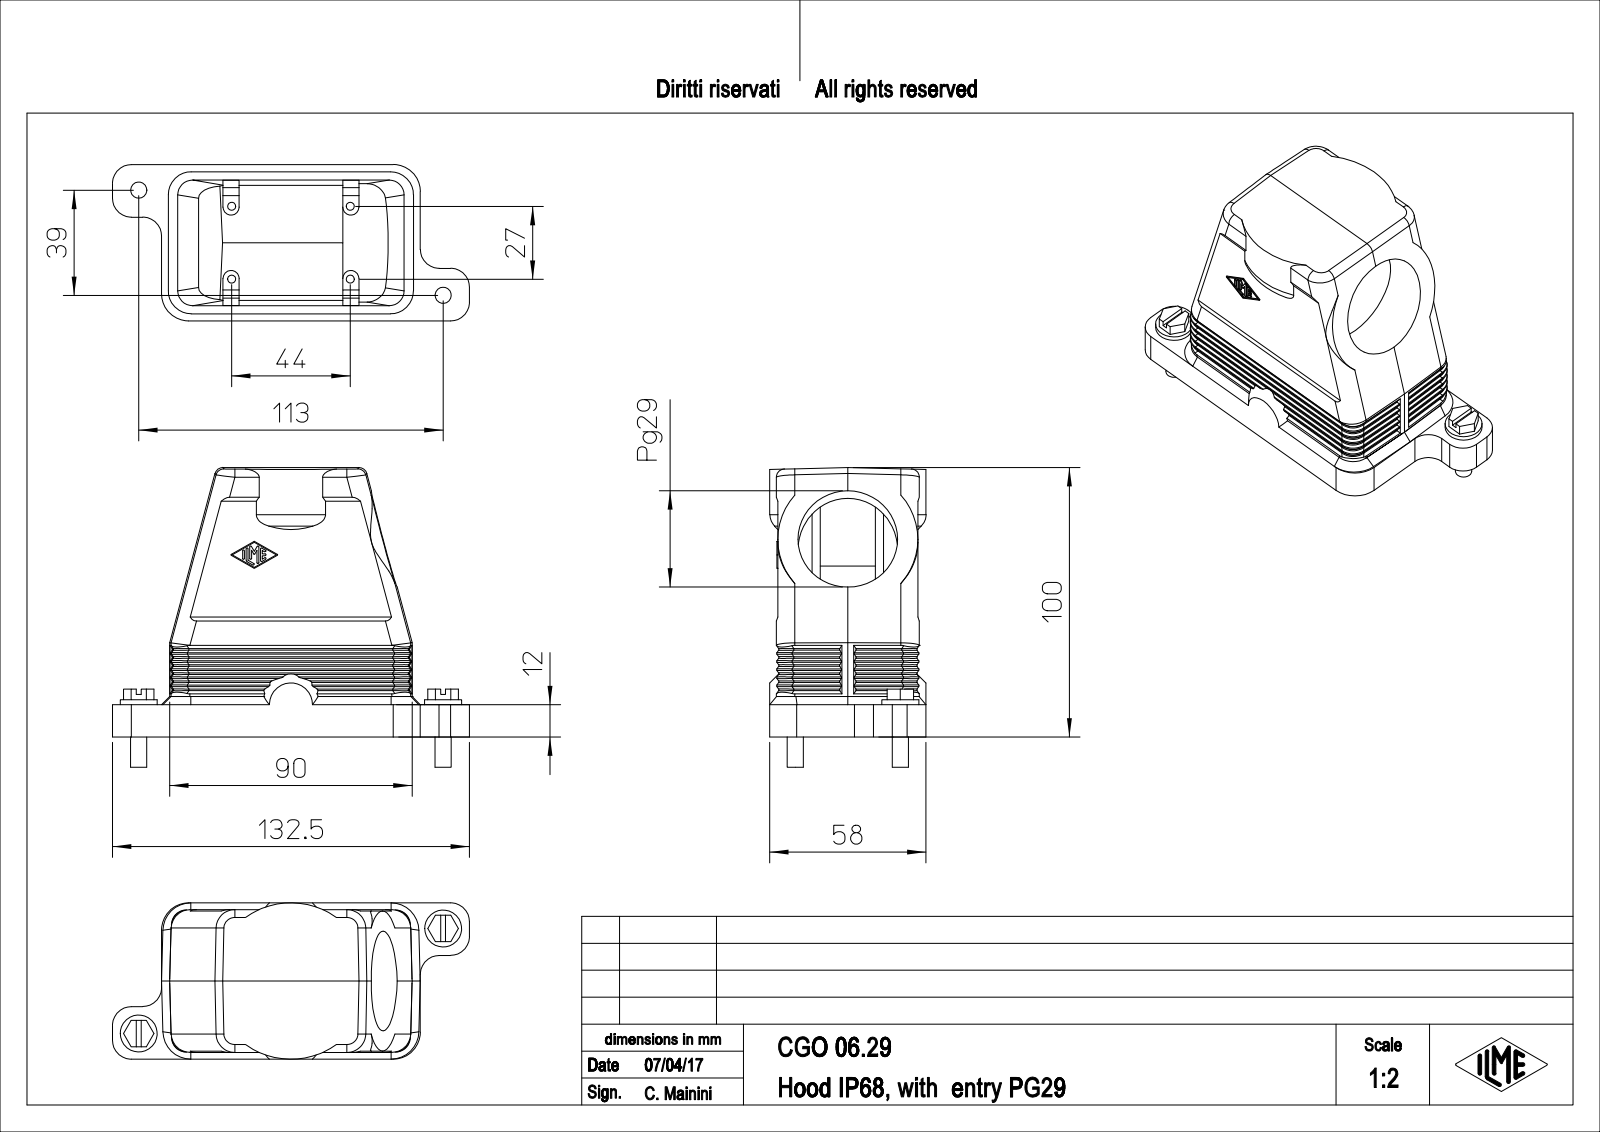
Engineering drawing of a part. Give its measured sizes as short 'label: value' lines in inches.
name: CGO_06.29
written by: PTC Creo Elements/Direct Modeling 19.0E 27-Jun-2016 (C) Parametric Technology GmbH (AUTOMOTIVE_DESIGN)
unit: in
bodies: 1 solid, 509 faces (245 planar, 202 cylindrical, 62 other)
size: 5.217 × 4.378 × 2.283
volume: 8.388 in³; area: 97.65 in²
holes: 4× ⌀0.118, 1× ⌀1.457
bosses: 2× ⌀0.539, 2× ⌀0.236
rounds: 66× R0.02, 62× R0.276, 15× R0.013, 6× R0.118, 4× R0.217, 4× R0.335, 3× R0.007, 2× R0.394
face distances: 0.118, 2.165, 2.047, 0.098, 0.236, 1.752, 0.131, 0.02, 2.185, 2.067
hole spacings: 1.063, 1.732, 2.032
